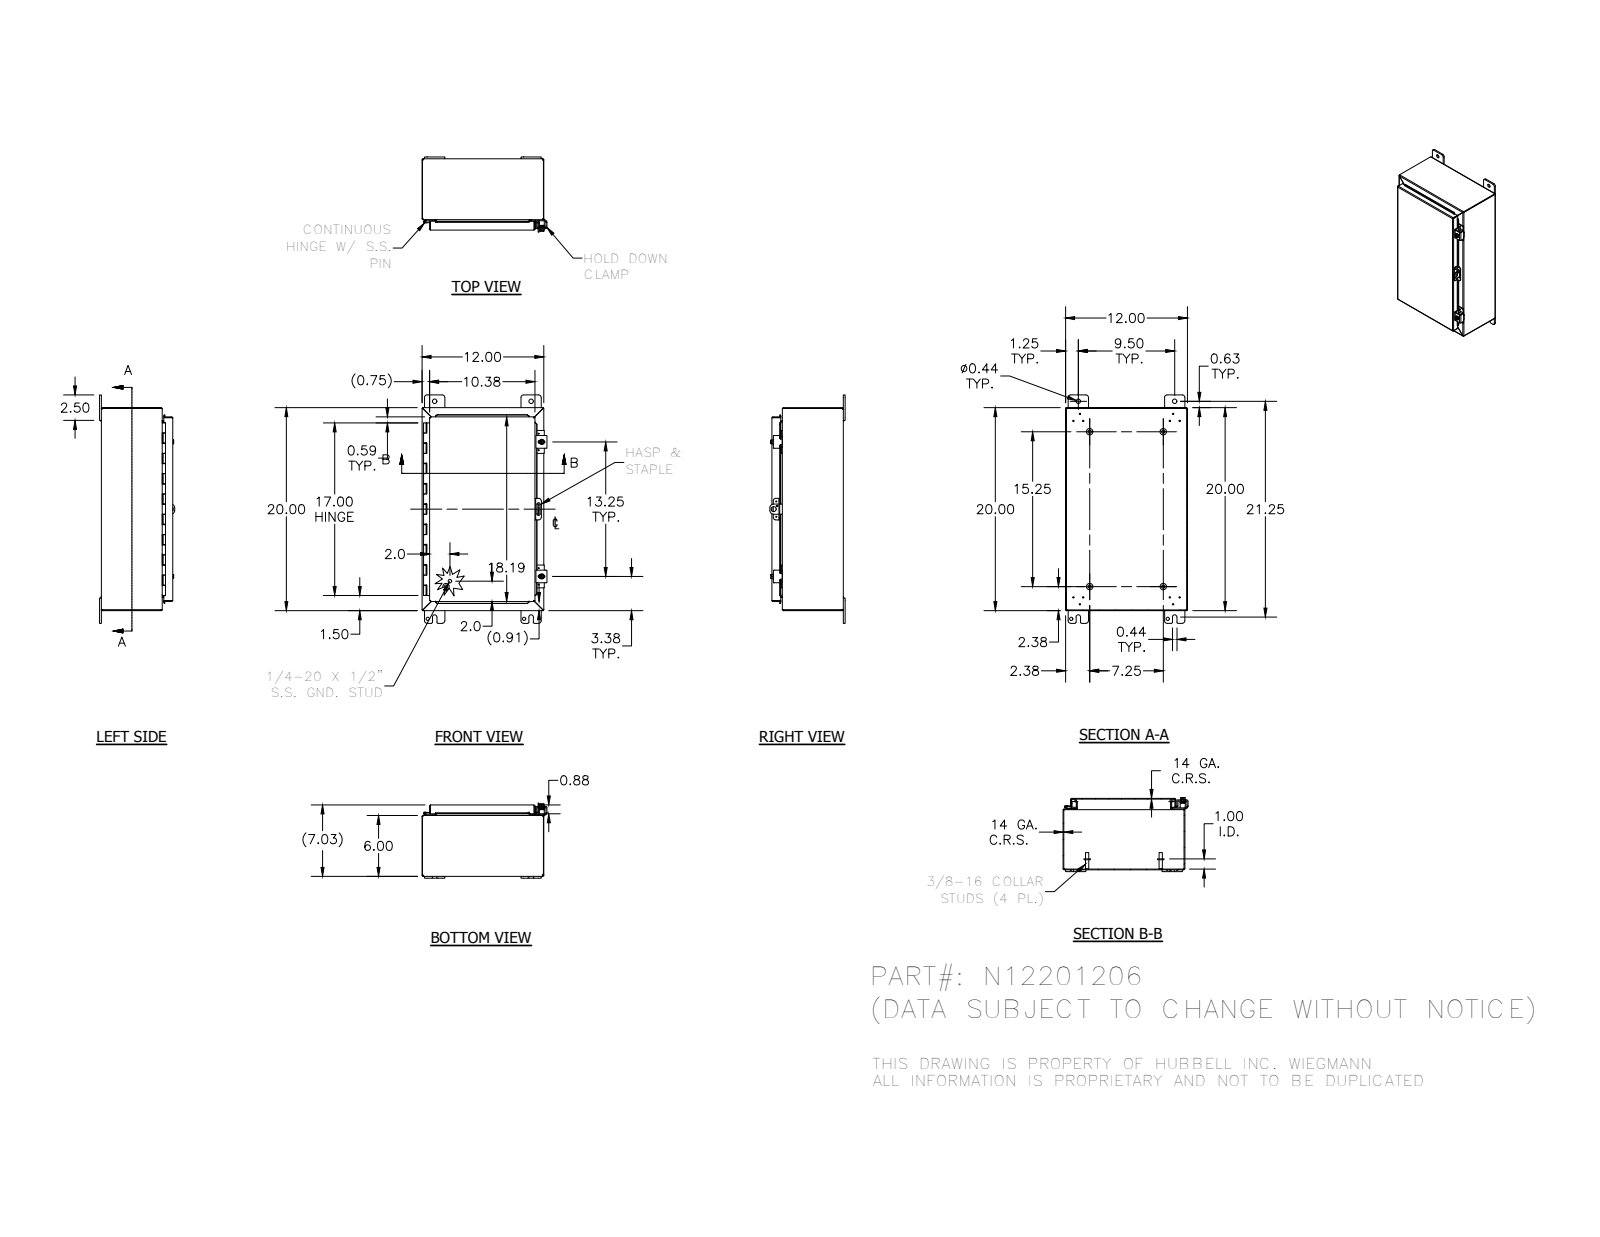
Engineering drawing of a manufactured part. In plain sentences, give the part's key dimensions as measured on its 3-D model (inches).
The part is named "N12201206; 34840; 38420; N12201206BKP (+8 more)". Its 3-D file was written by "Autodesk Inventor 2012 (AUTOMOTIVE_DESIGN)". It is 27 solids with 948 faces: 511 planar, 320 cylindrical and 117 other. Overall it measures 22.5 by 12.311 by 7.41 inches. Its volume is 86.14 cubic inches and its surface area 2 217 square inches. Round holes: 12 of diameter 0.12, 7 of diameter 0.11, 4 of diameter 0.313, 4 of diameter 0.438, 2 of diameter 0.211, 2 of diameter 0.281, 2 of diameter 0.3, 1 of diameter 0.125, 1 of diameter 0.156, 1 of diameter 0.5. Round bosses or shafts: 4 of diameter 0.625, 4 of diameter 0.33, 4 of diameter 0.25, 2 of diameter 0.52, 2 of diameter 0.5, 2 of diameter 0.35, 2 of diameter 0.115, 1 of diameter 0.337. Partial cylindrical surfaces (rounded edges, fillets, slot ends): 27 of radius 0.03, 25 of radius 0.063, 25 of radius 0.125, 25 of radius 0.25, 23 of radius 0.031, 23 of radius 0.105, 8 of radius 0.07, 4 of radius 0.1. The main face-to-face distances are 0.074, 6.959, 11.926, 6.885, 7.033, 5.926, 1.033, 19.926, 11.852, 12. The hole center spacings are 9.5, 18.077, 0.759, 0.839, 0.94, 0.969, 1.593, 1.995.
